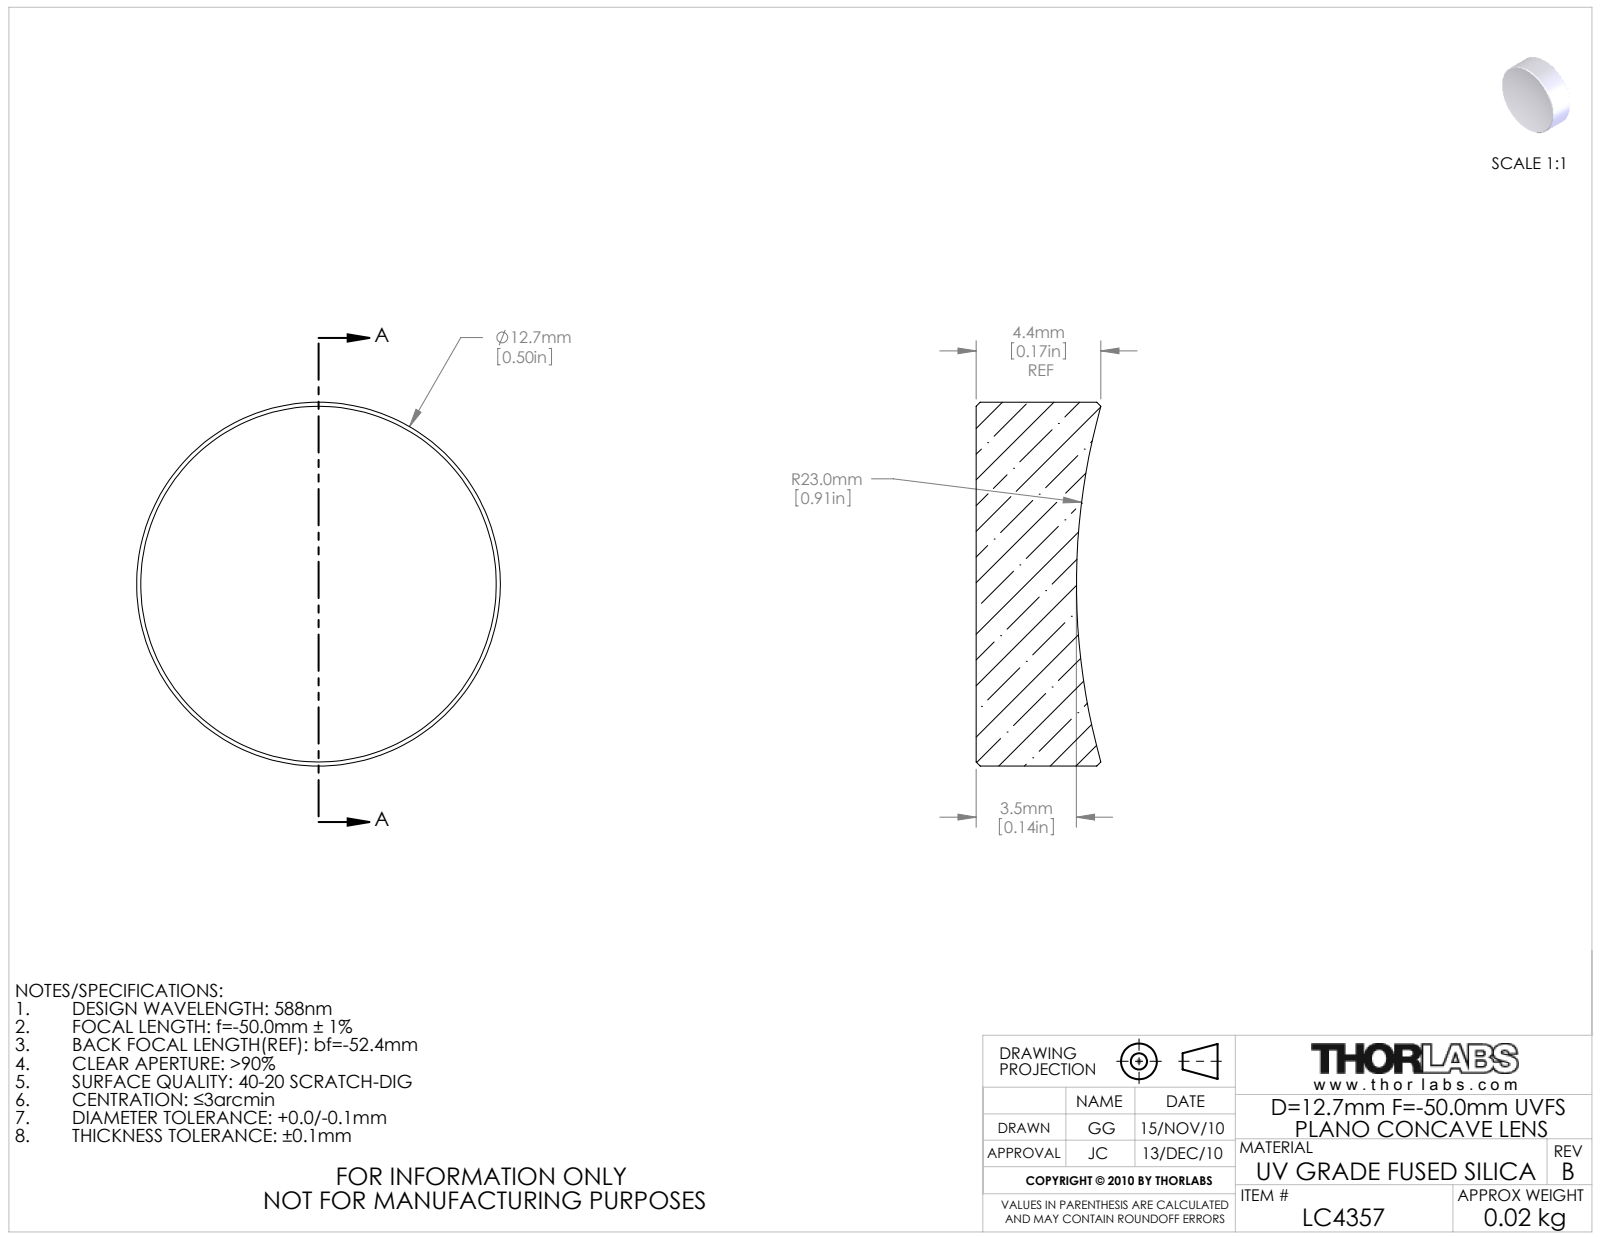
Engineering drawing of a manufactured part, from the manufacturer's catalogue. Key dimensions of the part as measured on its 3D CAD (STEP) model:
Part name (STEP PRODUCT): 3497-E0W
STEP written by: SolidWorks 2009 (AUTOMOTIVE_DESIGN)
Units: millimetres
Bodies: 1 solid, 9 faces (1 planar, 2 cylindrical, 6 other)
Overall size (bounding box): 12.7 × 12.7 × 4.35
Volume: 499 mm³ · Surface area: 423 mm²
Round bosses / shafts (diameter × count): ⌀12.7 ×1
